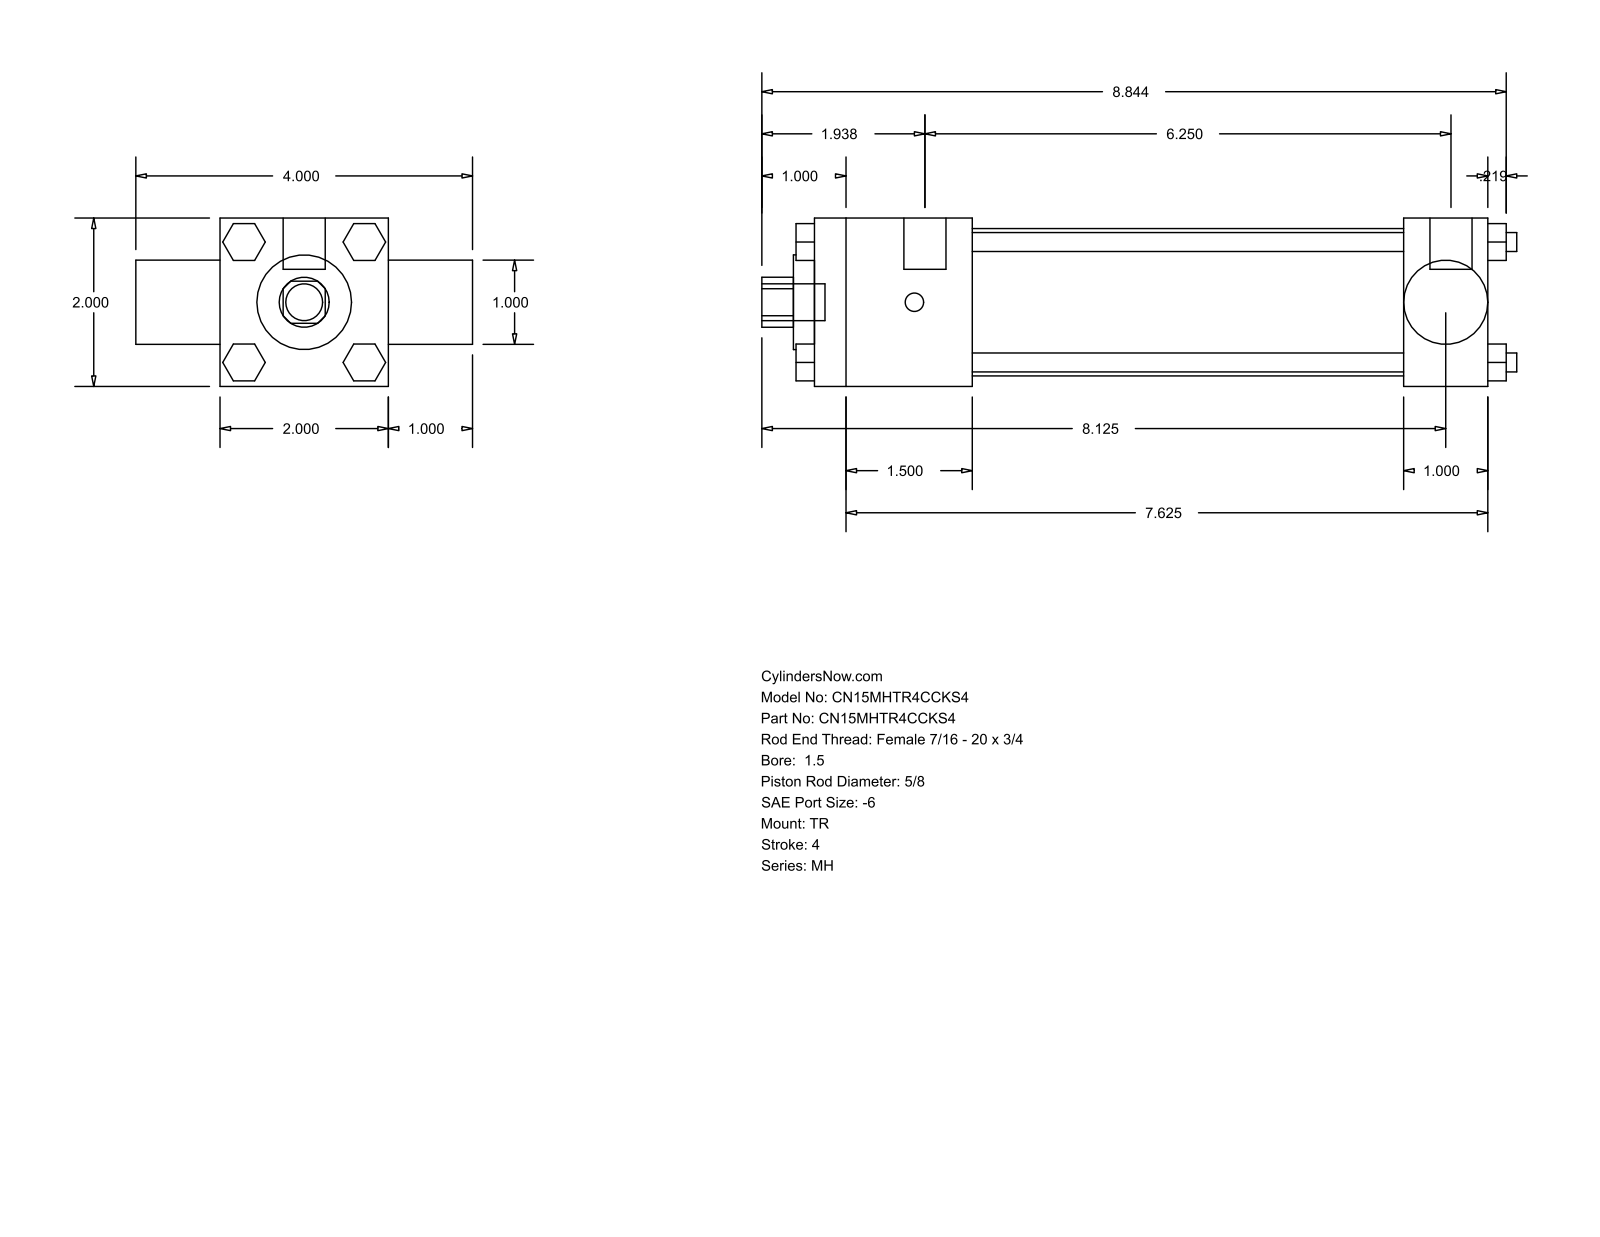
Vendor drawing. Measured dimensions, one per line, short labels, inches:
name: MH_TR__0150_0.625
written by: GSSL Pune (CONFIG_CONTROL_DESIGN)
unit: in
bodies: 0 solids, 120 faces (92 planar, 28 cylindrical, 0 other)
size: 8.969 × 4 × 2
holes: 1× ⌀0.625, 1× ⌀0.998, 1× ⌀1.125, 1× ⌀1.75
bosses: 4× ⌀0.225, 3× ⌀0.219, 2× ⌀0.5, 1× ⌀0.437
rounds: 1× R0.297
face distances: 2, 8, 1, 3, 1.875, 6.125, 7, 5.125, 1, 0.219
